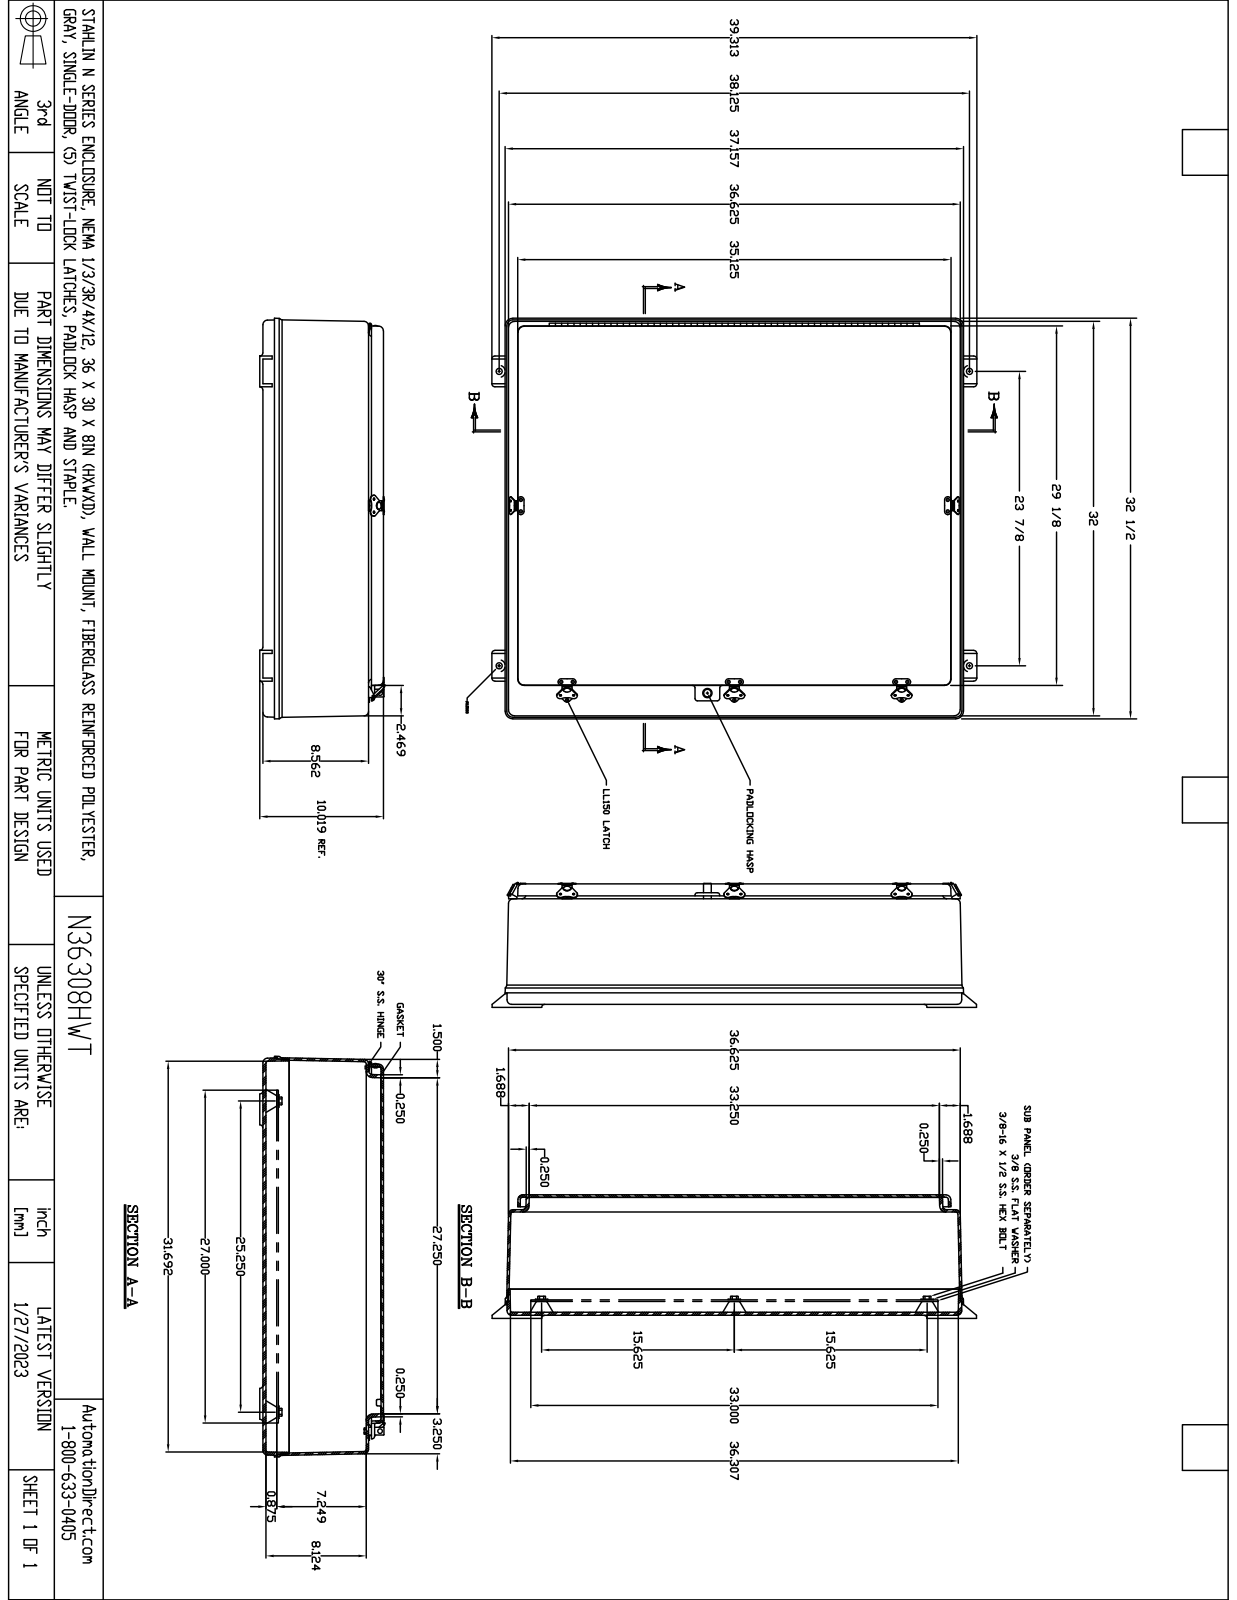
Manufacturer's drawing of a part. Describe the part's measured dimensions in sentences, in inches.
The part is named "T36308HWT". Its 3-D file was written by "SolidWorks 2018 (AUTOMOTIVE_DESIGN)". It is 63 solids with 1821 faces: 701 planar, 728 cylindrical and 392 other. Overall it measures 39.313 by 32.5 by 10.366 inches. Its volume is 823.1 cubic inches and its surface area 8 265 square inches. Round holes: 36 of diameter 0.13, 20 of diameter 0.063, 10 of diameter 0.138, 10 of diameter 0.187, 7 of diameter 0.065, 4 of diameter 0.563, 3 of diameter 0.156, 2 of diameter 0.135, 2 of diameter 0.433, 2 of diameter 0.51, 2 of diameter 0.51, 1 of diameter 0.065. Round bosses or shafts: 20 of diameter 0.14, 8 of diameter 0.297, 5 of diameter 0.5, 3 of diameter 0.2, 2 of diameter 0.135, 1 of diameter 0.25, 1 of diameter 0.201, 1 of diameter 0.135. Partial cylindrical surfaces (rounded edges, fillets, slot ends): 127 of radius 0.01, 24 of radius 0.25, 23 of radius 0.188, 20 of radius 0.03, 17 of radius 0.375, 13 of radius 0.313, 12 of radius 0.5, 10 of radius 0.125. The main face-to-face distances are 0.25, 0.188, 9.781, 9.531, 9.593, 9.343, 0.187, 0.188, 8.563, 8.375. The hole center spacings are 13.563, 9.5, 19.5, 1, 27.125, 3.474, 13.583, 15.625.
